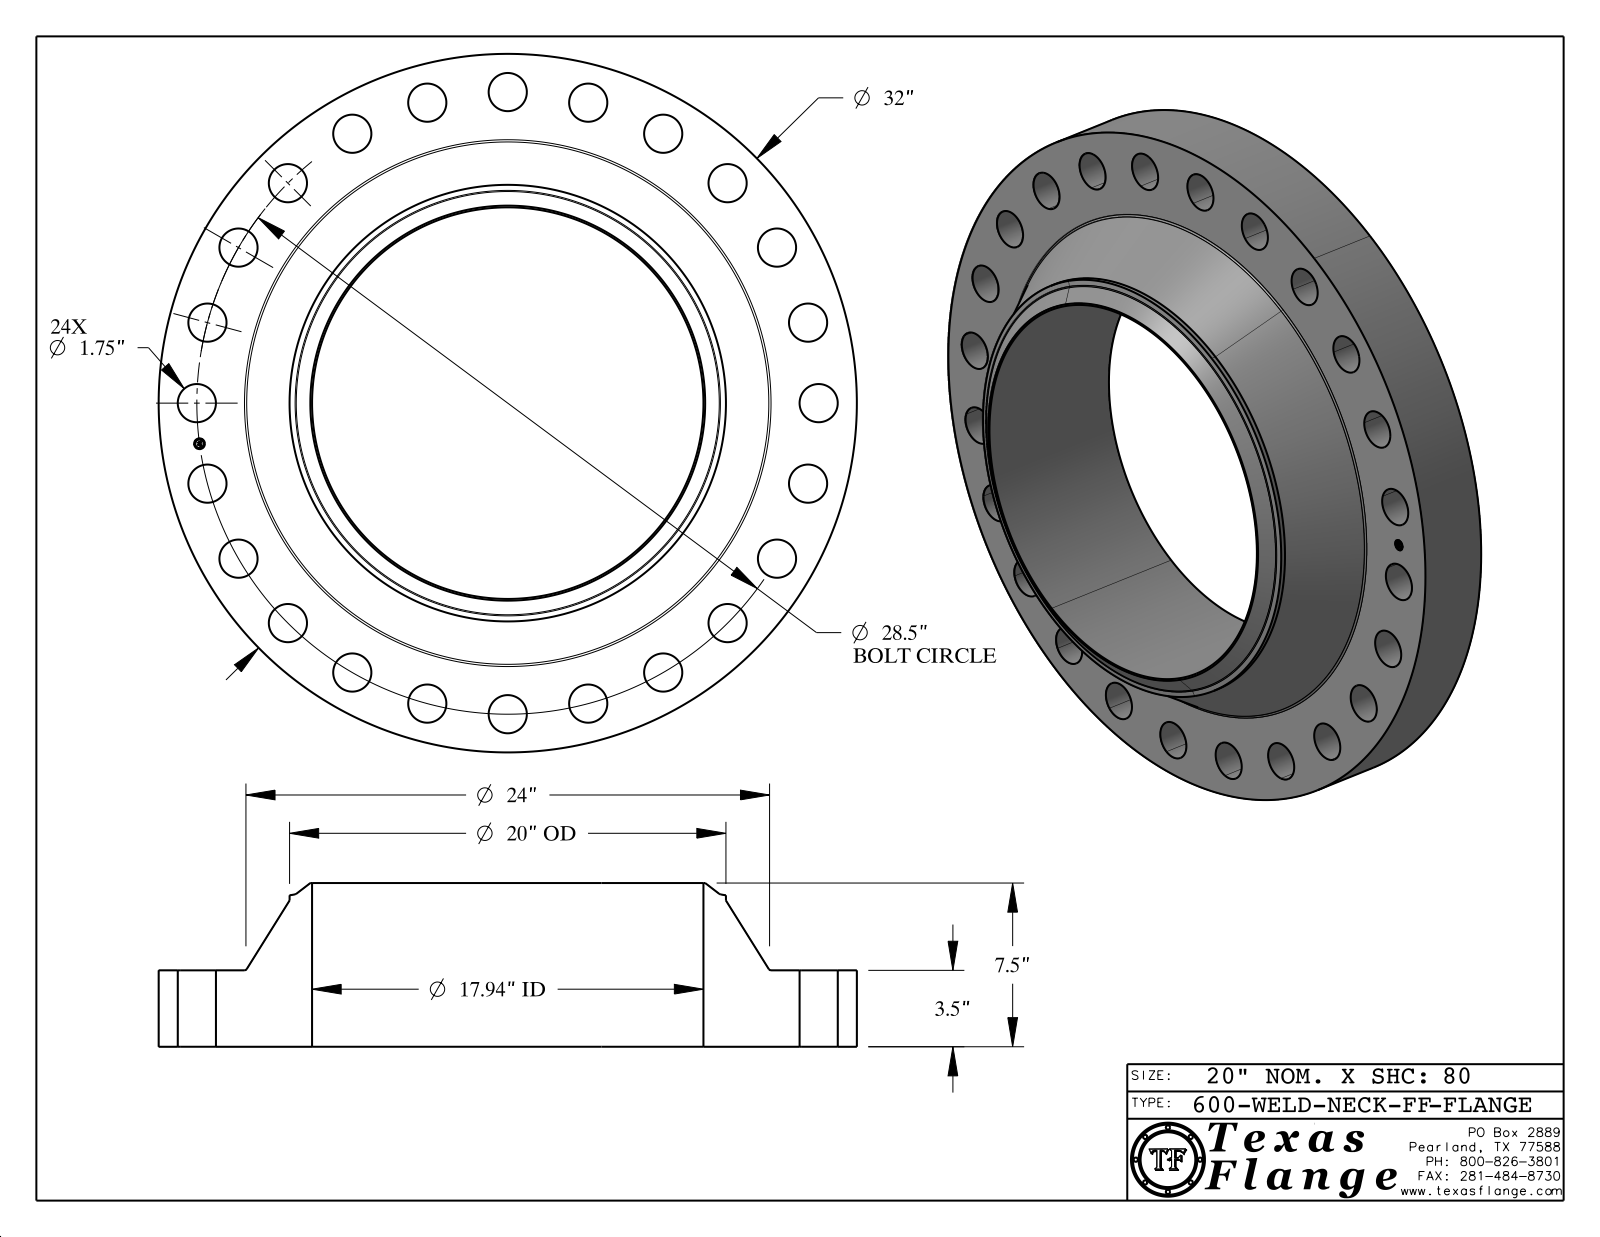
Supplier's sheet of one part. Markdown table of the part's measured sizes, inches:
| quantity | value |
| --- | --- |
| part name | 600-WELD-NECK-FF |
| STEP written by | CATIA V5 STEP AP214 (AUTOMOTIVE_DESIGN) |
| units | inches |
| bodies | 1 solid, 452 faces (368 planar, 74 cylindrical, 10 other) |
| overall size | 32 × 32 × 7.5 |
| volume | 2 169 in³ |
| surface area | 2 371 in² |
| round holes (diameter × count) | 1.75 × 24, 0.495 × 1, 17.938 × 1 |
| round bosses / shafts (diameter × count) | 0.03 × 8, 32 × 1, 20 × 1, 0.39 × 1 |
| main face-to-face distances | 3.5, 7.5, 4, 0.015, 3.485, 4.015, 0.148, 0.145, 0.027, 0.096 |
| hole center spacings | 14.25, 3.72, 7.376, 24.682, 26.331, 27.529, 20.153, 10.907 |
